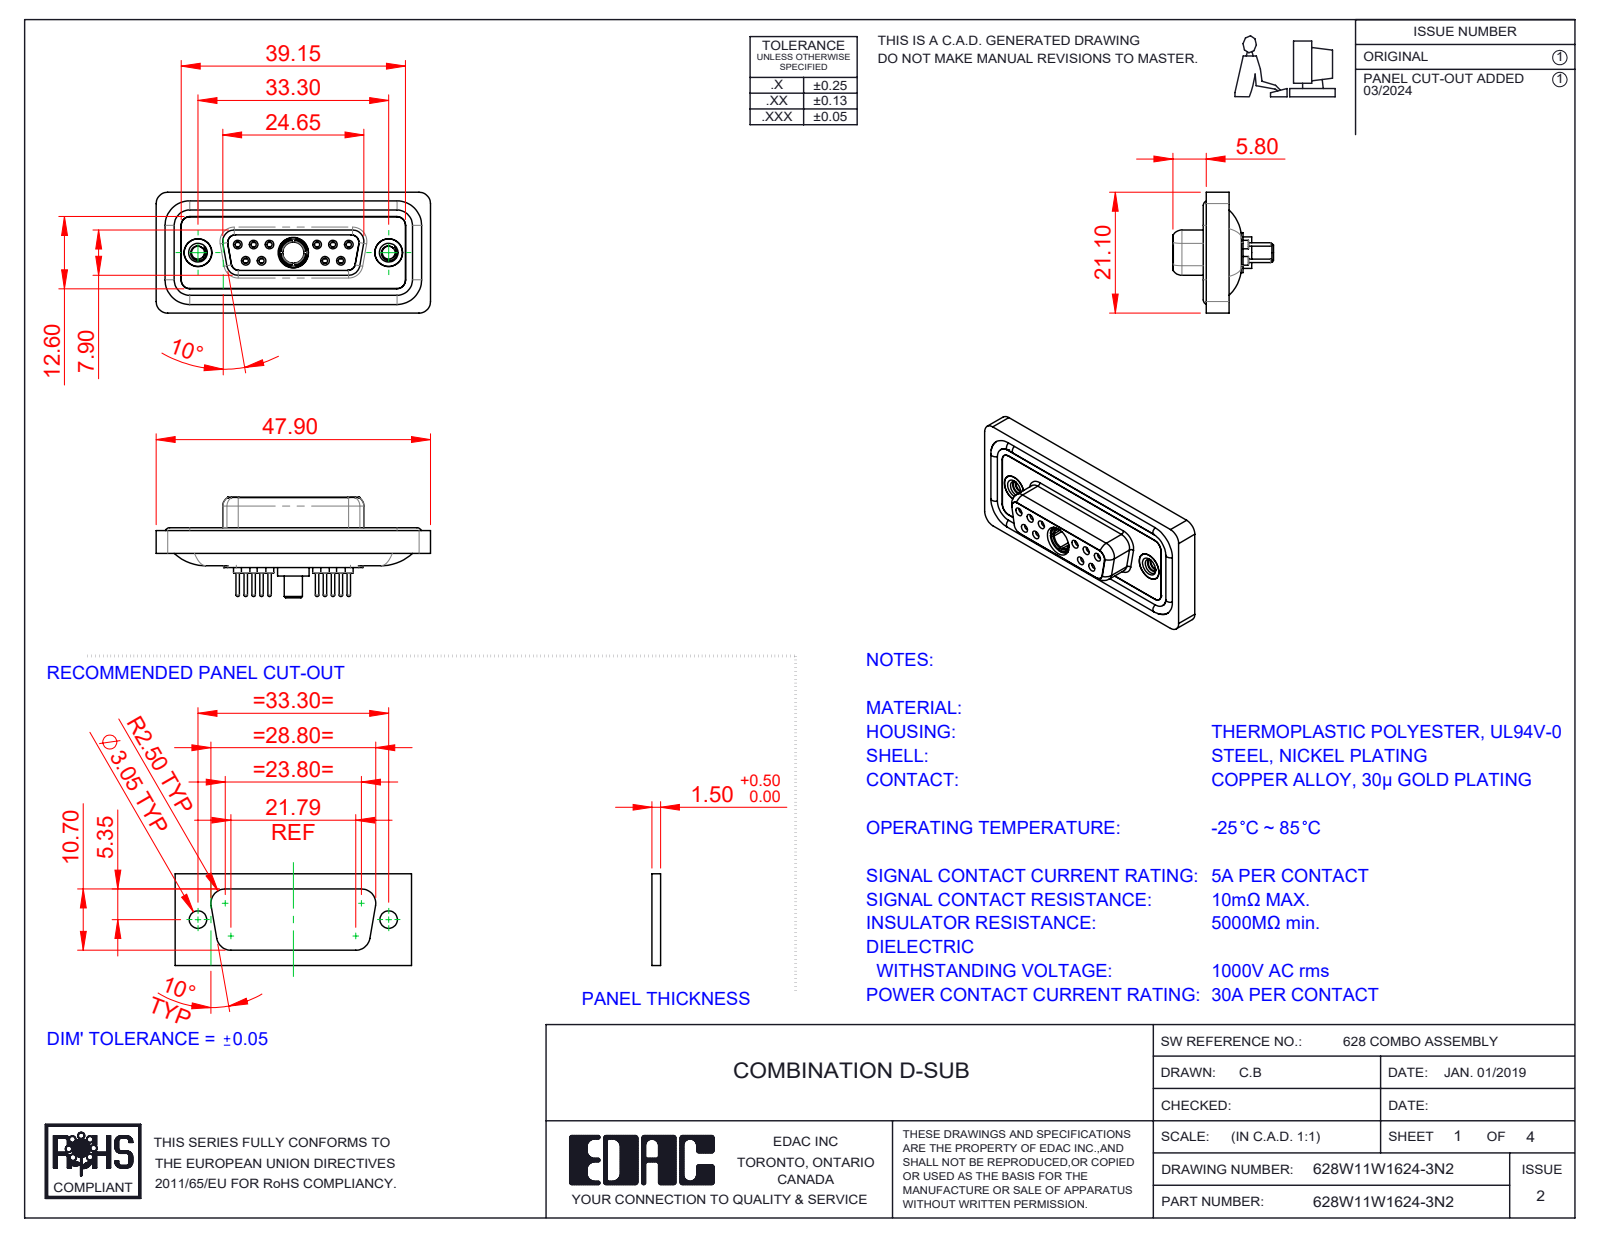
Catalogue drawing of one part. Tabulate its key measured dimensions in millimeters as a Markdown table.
| quantity | value |
| --- | --- |
| part name | 628Combo Shell Rear_15 Contacts; Power Socket_30A S; 628Combo Contact Row 1_24; 628W11W1624-3N2 (+5 more) |
| STEP written by | SolidWorks 2023 (CONFIG_CONTROL_DESIGN) |
| units | millimeters |
| bodies | 19 solids, 1010 faces (284 planar, 401 cylindrical, 325 other) |
| overall size | 47.9 × 21.1 × 17.55 |
| volume | 6 134 mm³ |
| surface area | 10 037 mm² |
| round holes (diameter × count) | 0.9 × 10, 1.1 × 10, 1.5 × 10, 2 × 10, 1.7 × 6, 1.6 × 4, 4.85 × 3, 2.26 × 2, 4 × 2, 4.05 × 2, 5 × 2, 3.7 × 1 |
| round bosses / shafts (diameter × count) | 2.2 × 10, 1.6 × 10, 0.6 × 10, 4.95 × 2, 4.8 × 2, 5.5 × 1, 5.2 × 1, 4.96 × 1 |
| partial cylindrical surfaces (radius × count) | 1.5 × 22, 2 × 20, 1.35 × 12, 1.6 × 8, 0.25 × 4, 0.5 × 4, 0.6 × 4, 0.65 × 4 |
| main face-to-face distances | 0.4, 1.6, 1.8, 2.9, 0.5, 1.1, 5.65, 7.45, 6.6, 7.05 |
| hole center spacings | 3.16, 2.77, 13.85, 11.08, 16.62, 5.03, 5.04, 5.54 |
